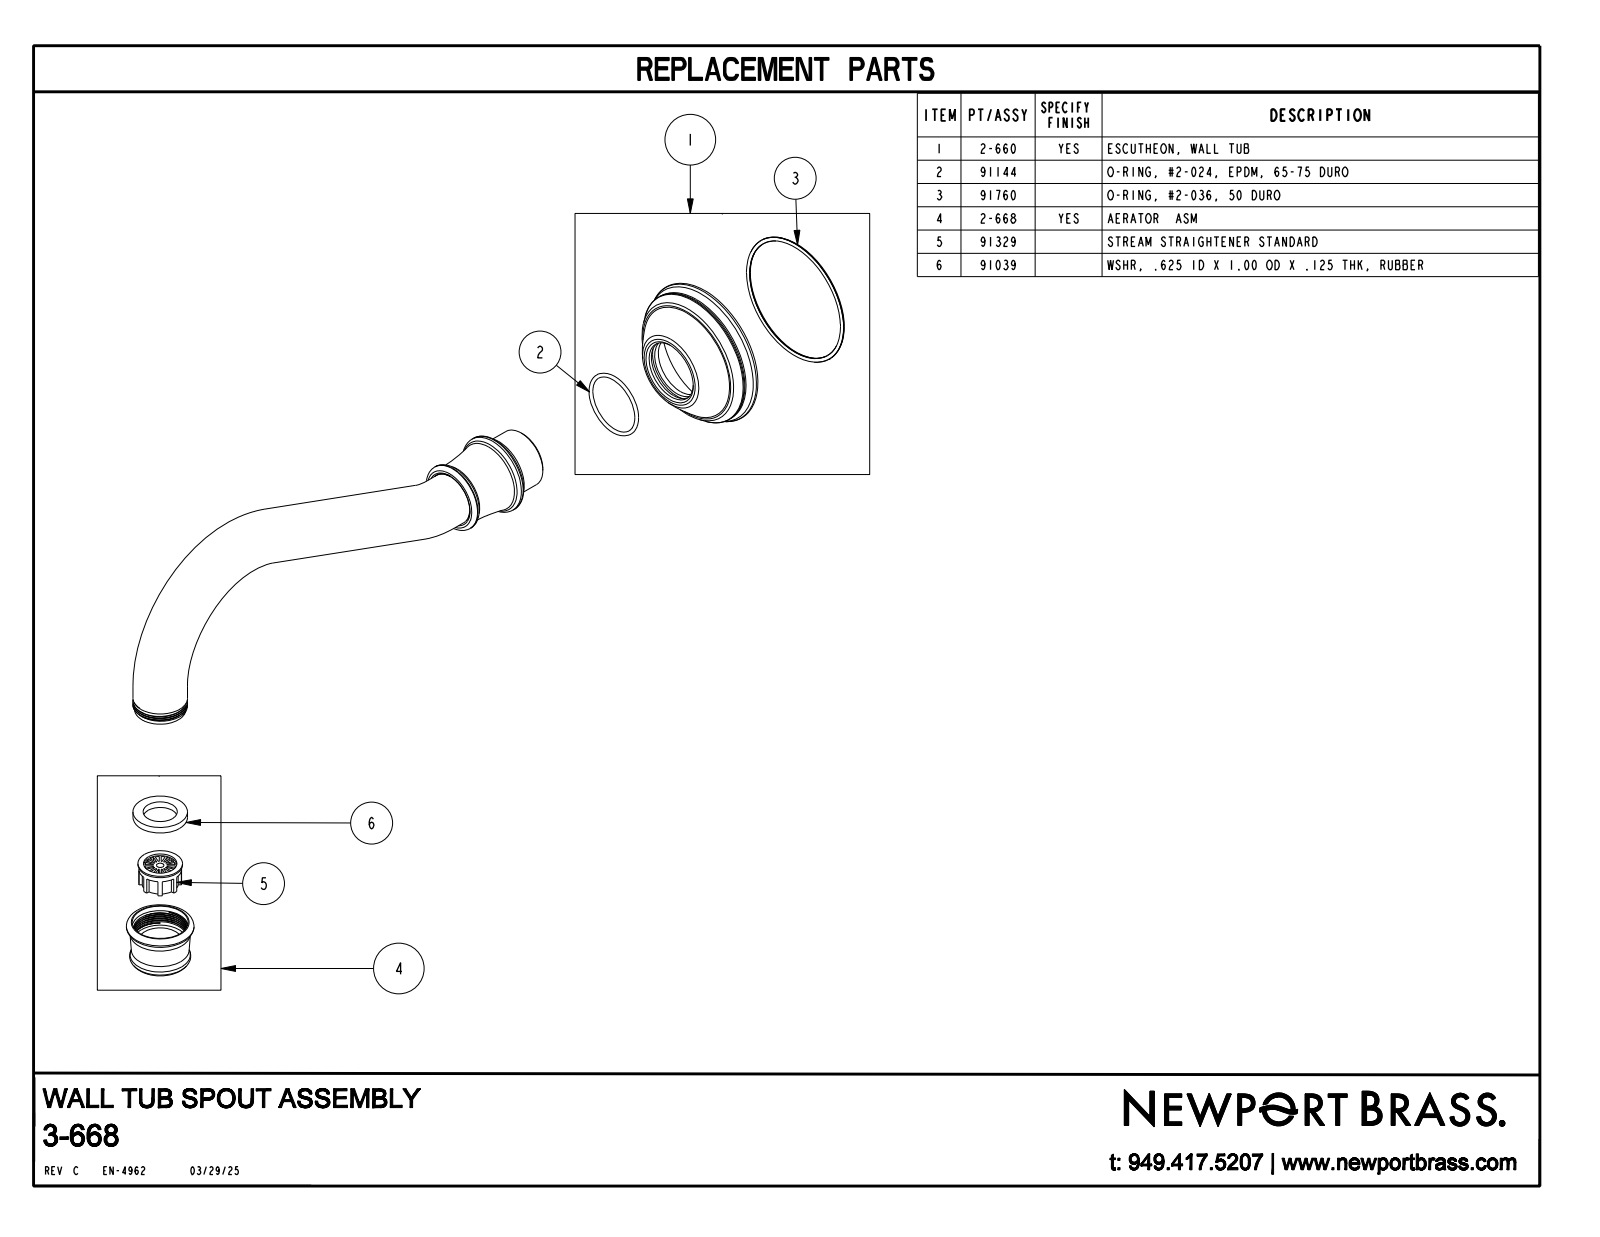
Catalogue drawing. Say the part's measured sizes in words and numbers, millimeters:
The part is named "3-668". Its 3-D file was written by "CREO PARAMETRIC BY PTC INC, 2018400 (AUTOMOTIVE_DESIGN)". It is 1 solid with 71 faces: 7 planar, 12 cylindrical and 52 other. Overall it measures 262.2 by 93.9 by 70.4 millimeters. Its volume is 219 900 cubic millimeters and its surface area 34 570 square millimeters. Round bosses or shafts: 3 of diameter 25.4, 1 of diameter 38.1, 1 of diameter 33.5, 1 of diameter 33. The main face-to-face distances are 55.9, 25.5, 30.4, 12.2, 13.3, 43.7, 21.6, 23.5, 11.3, 2.
